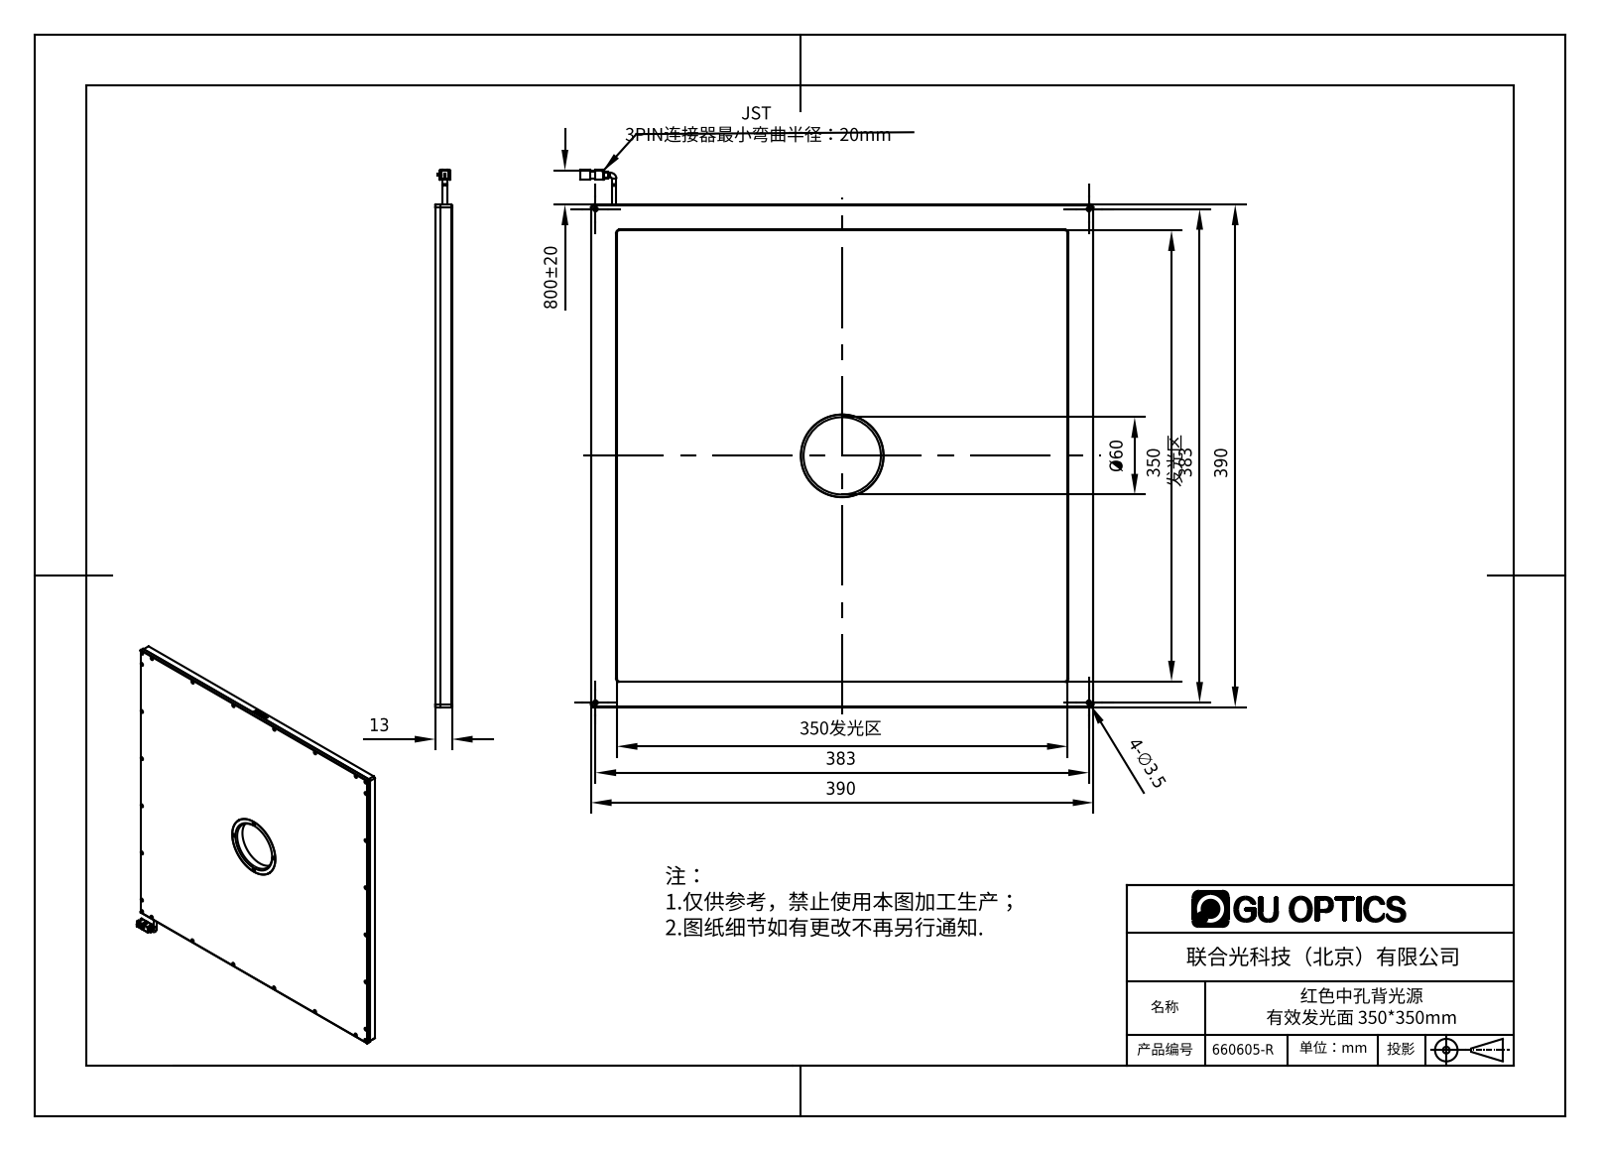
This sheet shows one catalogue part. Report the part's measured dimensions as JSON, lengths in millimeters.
{"part_name": "660605-R", "step_written_by": "SolidWorks 2016 (AUTOMOTIVE_DESIGN)", "units": "millimeters", "bodies": {"solids": 6, "faces": 510, "planar": 177, "cylindrical": 170, "other": 163}, "overall_size": [417, 398.5, 13], "volume_mm3": 1515000, "surface_area_mm2": 673989, "round_holes": [[2.4, 28], [1.6, 24], [3.5, 4], [60, 1], [64.2, 1], [74, 1]], "round_bosses_or_shafts": [[3.5, 2], [73.8, 1], [64, 1]], "partial_cylinders_radius": [[0.5, 8], [2, 8], [1, 4], [3, 4], [1.5, 2]], "face_to_face_distances": [4, 6, 10, 9, 3, 13, 0.5, 6.5, 2.5, 10.5], "hole_center_spacings": [70, 390.33, 140, 408.72, 210, 384, 437.67, 16.51]}
